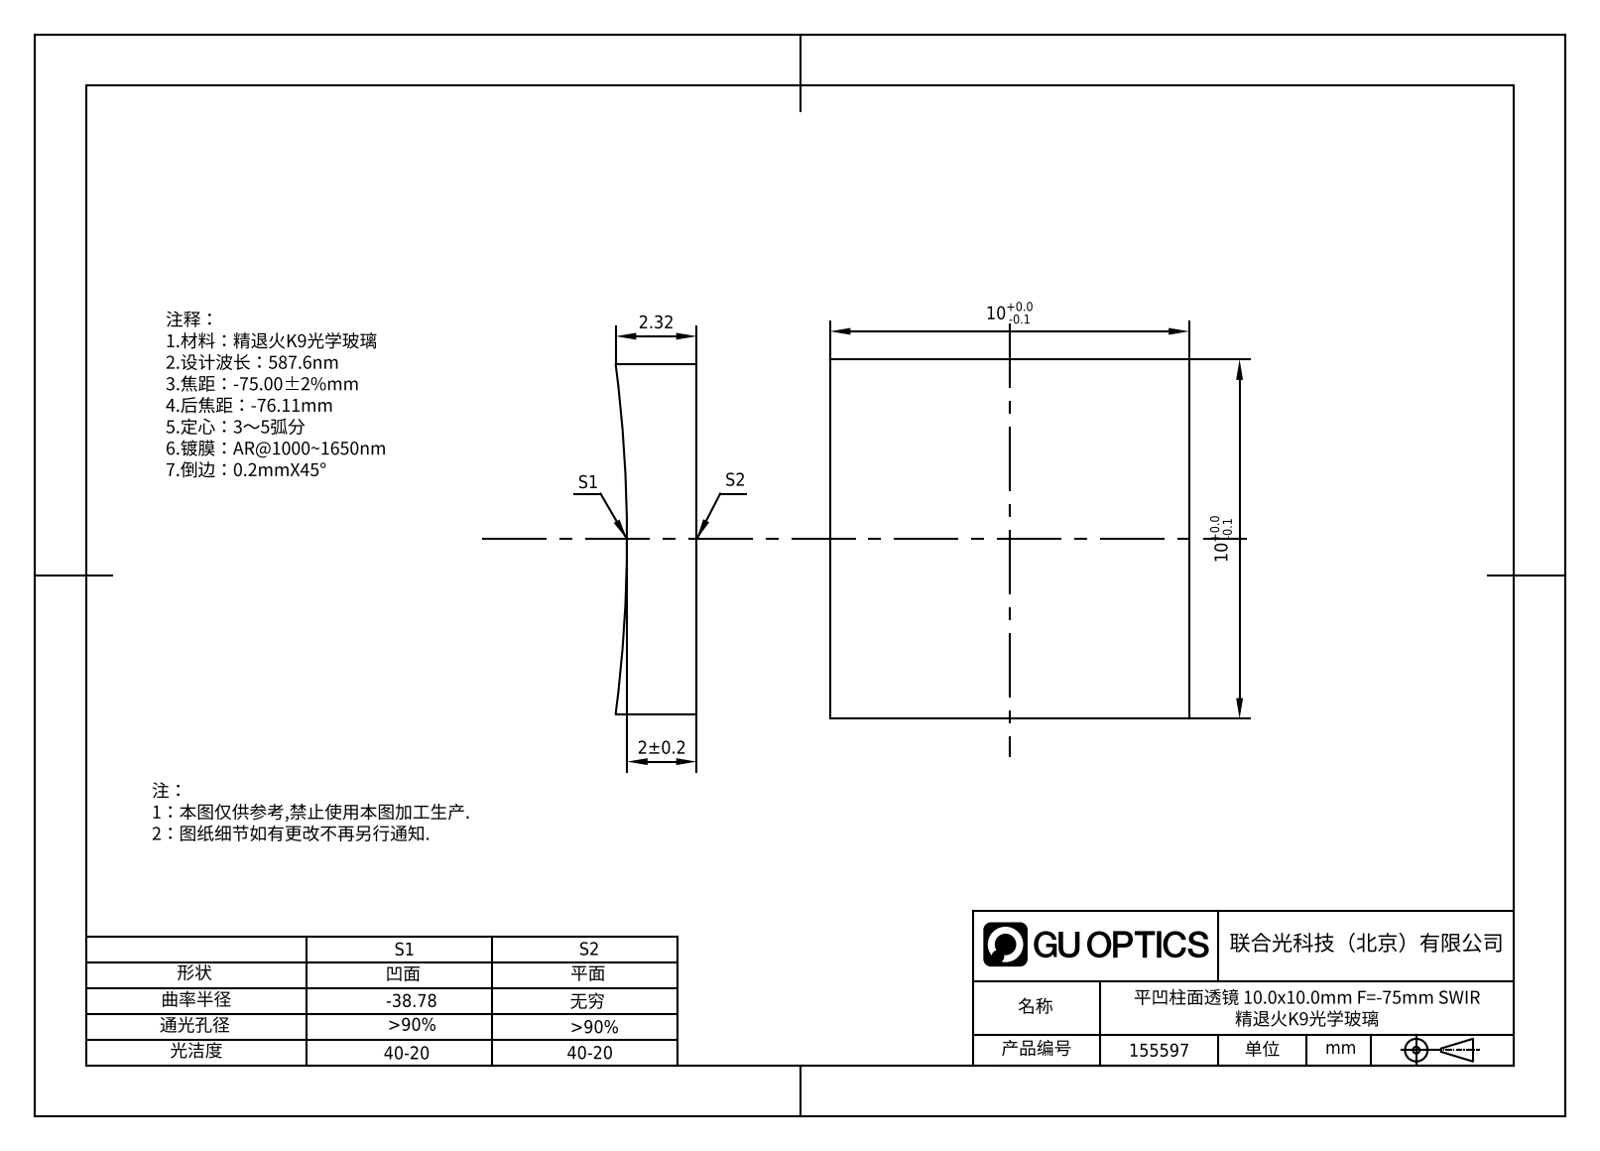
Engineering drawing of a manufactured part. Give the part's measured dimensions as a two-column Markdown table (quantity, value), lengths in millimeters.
| quantity | value |
| --- | --- |
| part name | 155567 |
| STEP written by | SolidWorks 2020 (CONFIG_CONTROL_DESIGN) |
| units | millimeters |
| bodies | 1 solid, 6 faces (5 planar, 1 cylindrical, 0 other) |
| overall size | 10 × 10 × 2.32 |
| volume | 210 mm³ |
| surface area | 289 mm² |
| partial cylindrical surfaces (radius × count) | 38.78 × 1 |
| main face-to-face distances | 10 |
